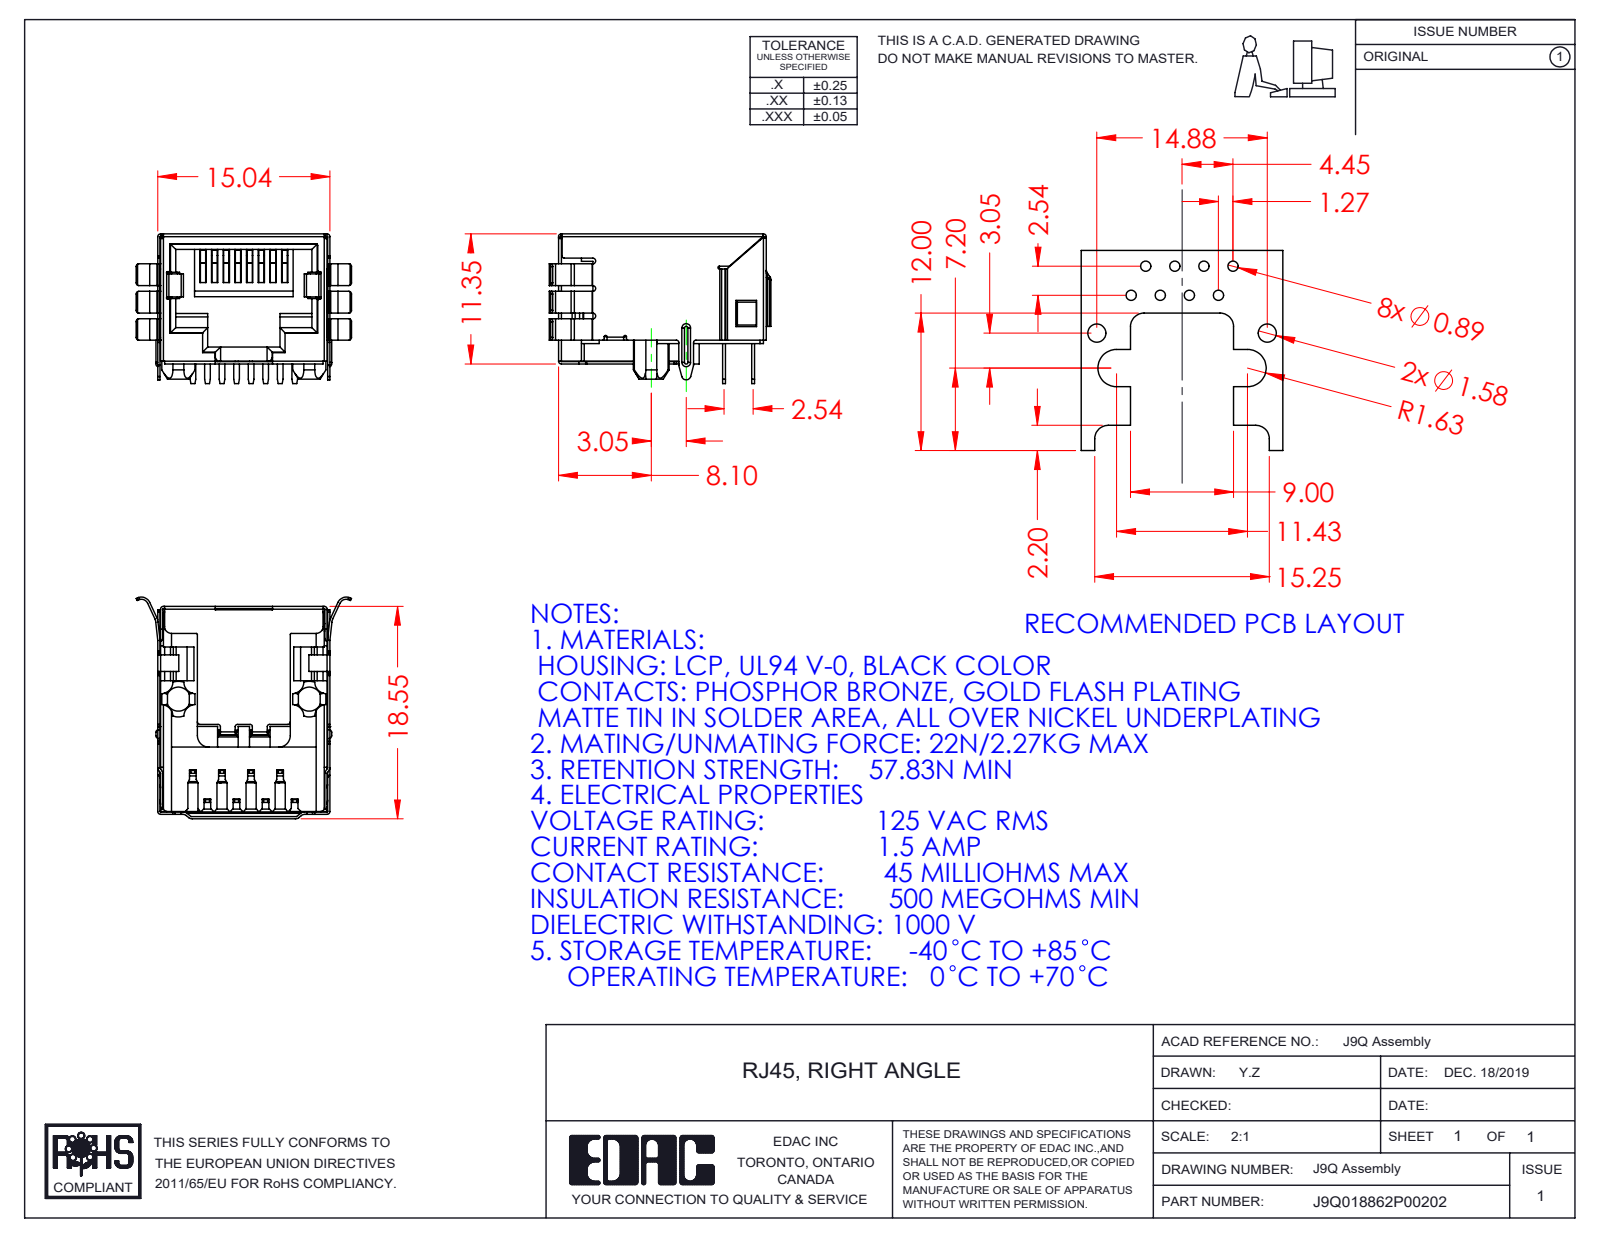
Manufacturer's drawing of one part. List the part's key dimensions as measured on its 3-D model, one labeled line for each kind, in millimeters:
Part name (STEP PRODUCT): 9Q Shield; 9Q Insulator; 9Q Contact Lock; J9Q018862P00202 (+1 more)
STEP written by: SolidWorks 2016 (CONFIG_CONTROL_DESIGN)
Units: millimetres
Bodies: 11 solids, 1339 faces (949 planar, 369 cylindrical, 21 other)
Overall size (bounding box): 19.36 × 18.81 × 13.07
Volume: 1 193 mm³ · Surface area: 4 818 mm²
Partial cylindrical surfaces — rounded edges, fillets, slot ends (radius × count): R0.1 ×43, R0.2 ×35, R0.25 ×34, R0.15 ×24, R0.5 ×19, R0.3 ×14, R0.6 ×8, R1.05 ×8
Main face-to-face distances: 14.59, 14.54, 14.84, 14.34, 14.79, 0.5, 11.15, 14.29, 14.64, 15.04
